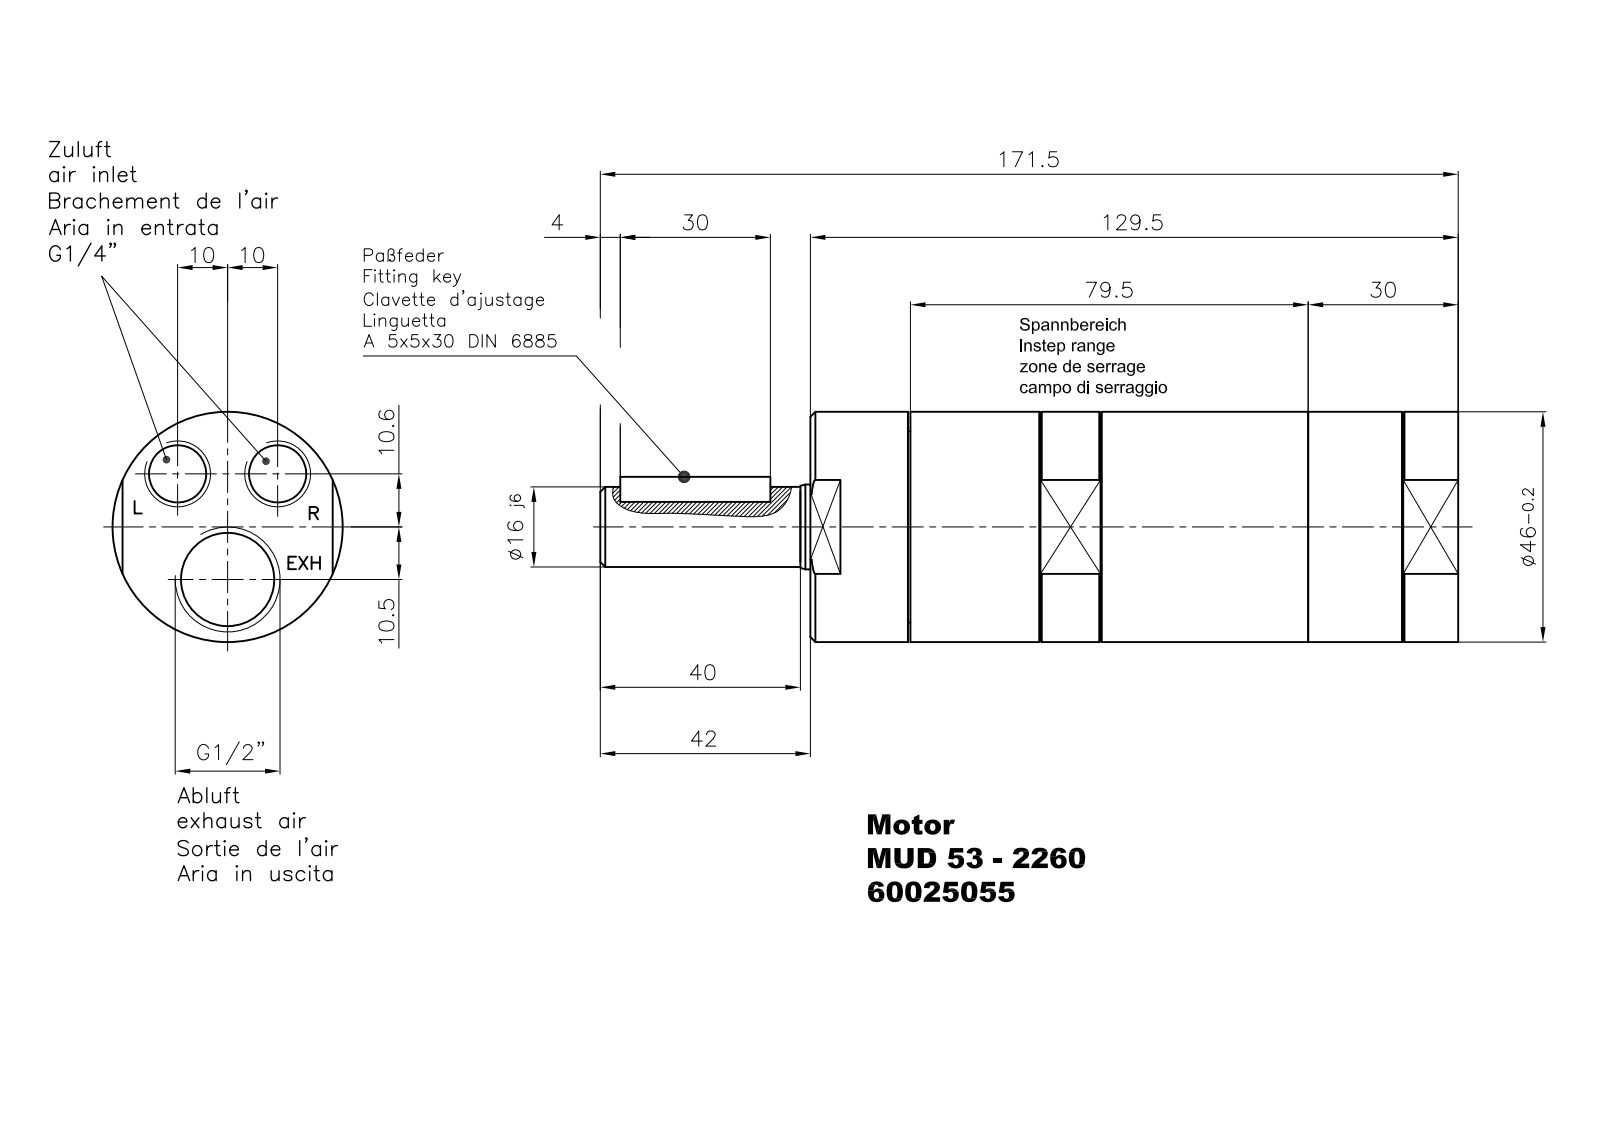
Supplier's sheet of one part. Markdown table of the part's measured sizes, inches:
| quantity | value |
| --- | --- |
| part name | MUD 53-171 |
| STEP written by | Autodesk Inventor 2012 (AUTOMOTIVE_DESIGN) |
| units | inches |
| bodies | 1 solid, 135 faces (92 planar, 18 cylindrical, 25 other) |
| overall size | 6.752 × 1.811 × 1.811 |
| volume | 13.13 in³ |
| surface area | 43.03 in² |
| round holes (diameter × count) | 0.451 × 2, 0.063 × 1, 0.689 × 1, 0.733 × 1 |
| round bosses / shafts (diameter × count) | 1.811 × 1, 1.502 × 1, 0.667 × 1, 0.63 × 1 |
| partial cylindrical surfaces (radius × count) | 0.098 × 2 |
| main face-to-face distances | 5.098, 1.654, 1.181, 3.917, 0.768, 3.15, 4.331, 4.311, 0.787, 0.02 |
| hole center spacings | 0.574, 0.919, 0.413, 0.787 |
